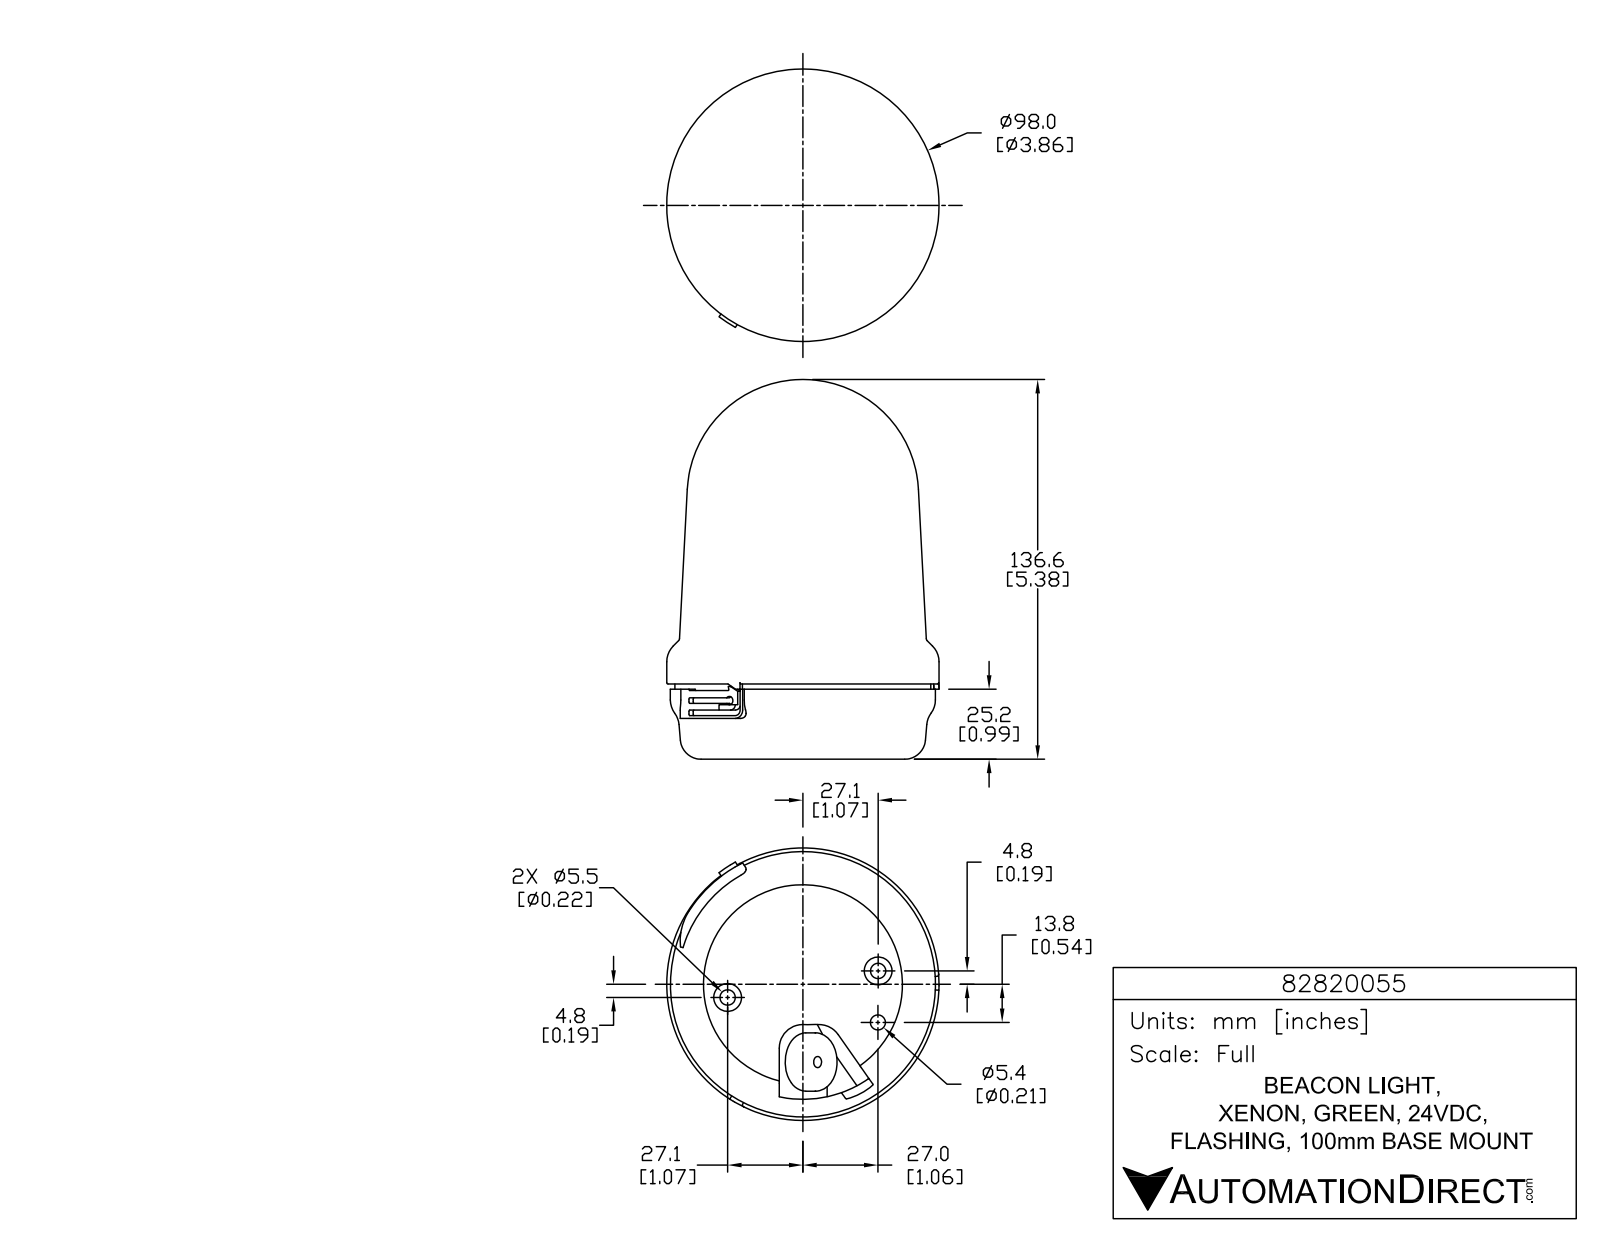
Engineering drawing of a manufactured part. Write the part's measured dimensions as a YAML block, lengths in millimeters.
part_name: "82820055"
step_written_by: "SolidWorks 2015 (AUTOMOTIVE_DESIGN)"
units: millimeters
bodies: {solids: 1, faces: 872, planar: 566, cylindrical: 204, other: 102}
overall_size: [136.6, 98, 98]
volume: 732300
surface_area: 47520
round_holes:
  - {diameter: 1.5, count: 3}
  - {diameter: 5.5, count: 2}
  - {diameter: 4, count: 1}
  - {diameter: 5.4, count: 1}
  - {diameter: 71.6, count: 1}
round_bosses_or_shafts:
  - {diameter: 8.6, count: 3}
  - {diameter: 2.1, count: 3}
  - {diameter: 10, count: 2}
  - {diameter: 98, count: 1}
  - {diameter: 95.4, count: 1}
  - {diameter: 92.1, count: 1}
  - {diameter: 21, count: 1}
partial_cylinders:
  - {radius: 0.1, count: 9}
  - {radius: 0.1, count: 6}
  - {radius: 0.3, count: 6}
  - {radius: 0.3, count: 6}
  - {radius: 0.3, count: 6}
  - {radius: 5, count: 6}
  - {radius: 0.5, count: 5}
  - {radius: 1, count: 4}
face_to_face_distances: [26.5, 24.7, 1.9, 0.5, 25.2, 27.1, 6, 14.7, 14.2, 10.5]
hole_center_spacings: [27.5, 18.5, 30.3, 54.8, 55]
